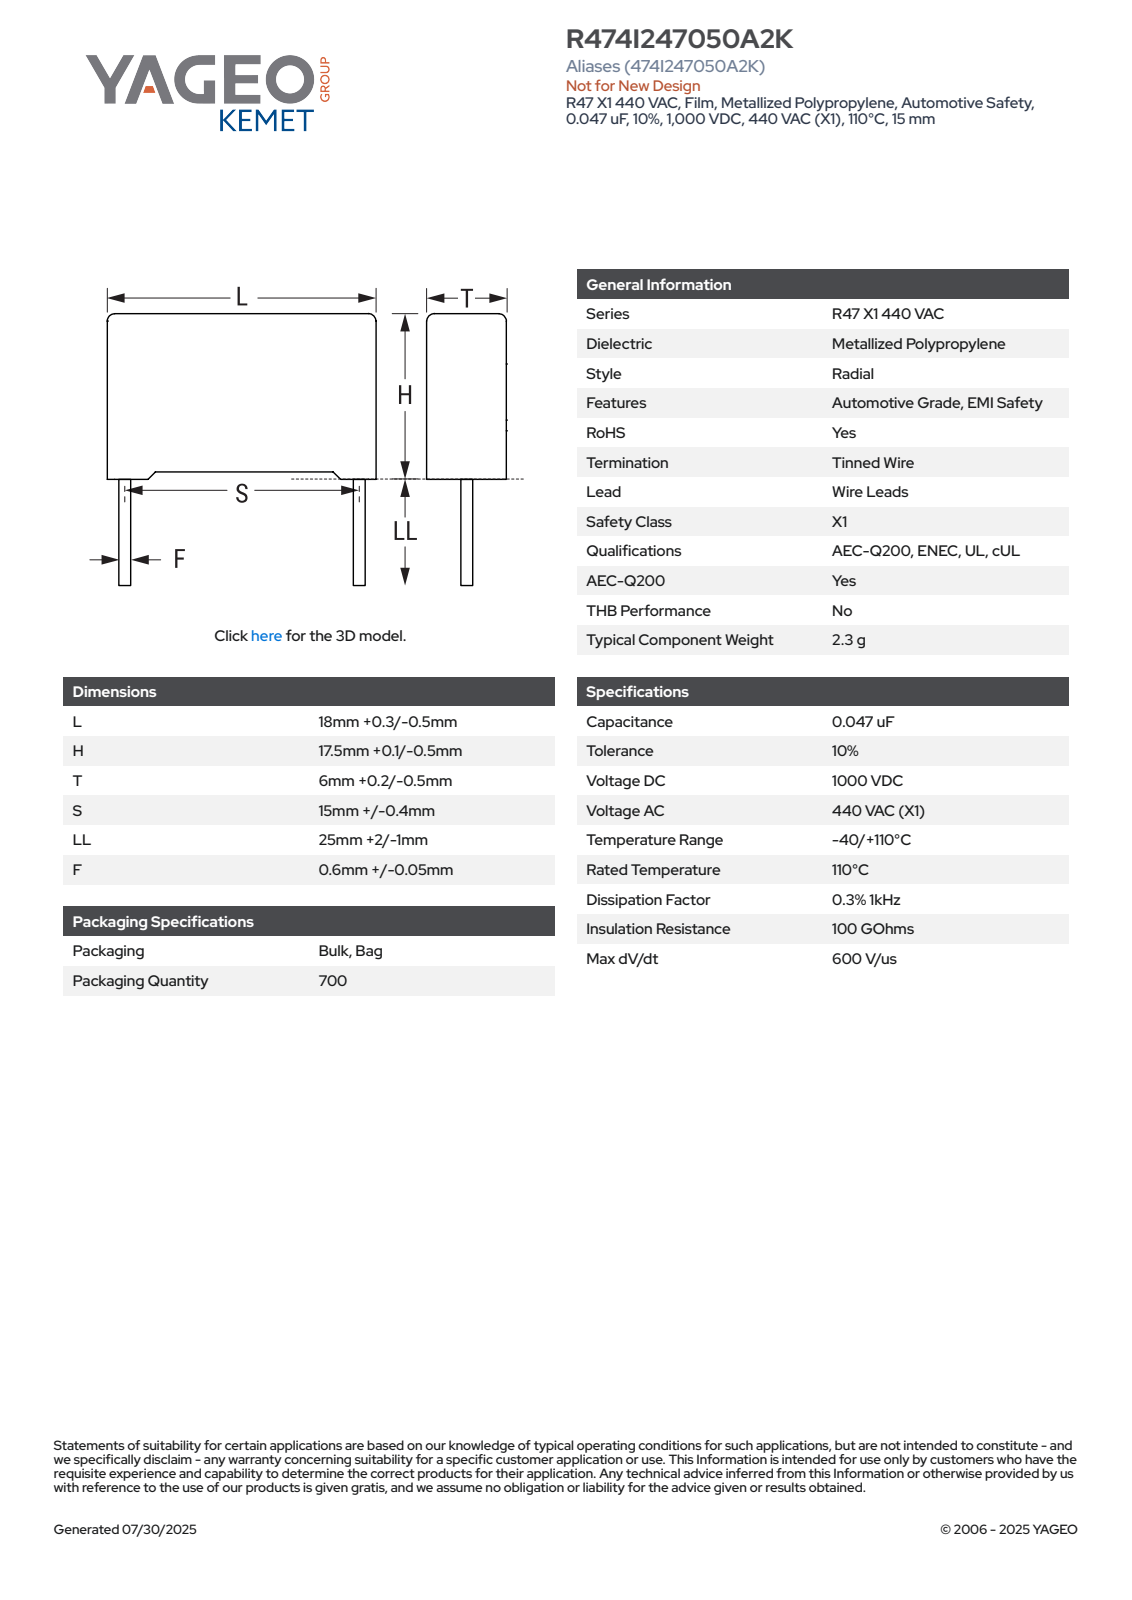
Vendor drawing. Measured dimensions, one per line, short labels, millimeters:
name: CFR_RB2_18X17.5X6_L18.3H17.6T6.2S15LL27F0.65
written by: SolidWorks 2021 (AUTOMOTIVE_DESIGN)
unit: mm
bodies: 4 solids, 85 faces (77 planar, 8 cylindrical, 0 other)
size: 44.6 × 18.3 × 6.21
volume: 1 940 mm³; area: 1 223 mm²
bosses: 2× ⌀0.65
rounds: 4× R0.5
face distances: 6.2, 18.3, 16.85, 0.61, 0.75, 17.6, 16.99, 5.59, 17.69, 4.98
